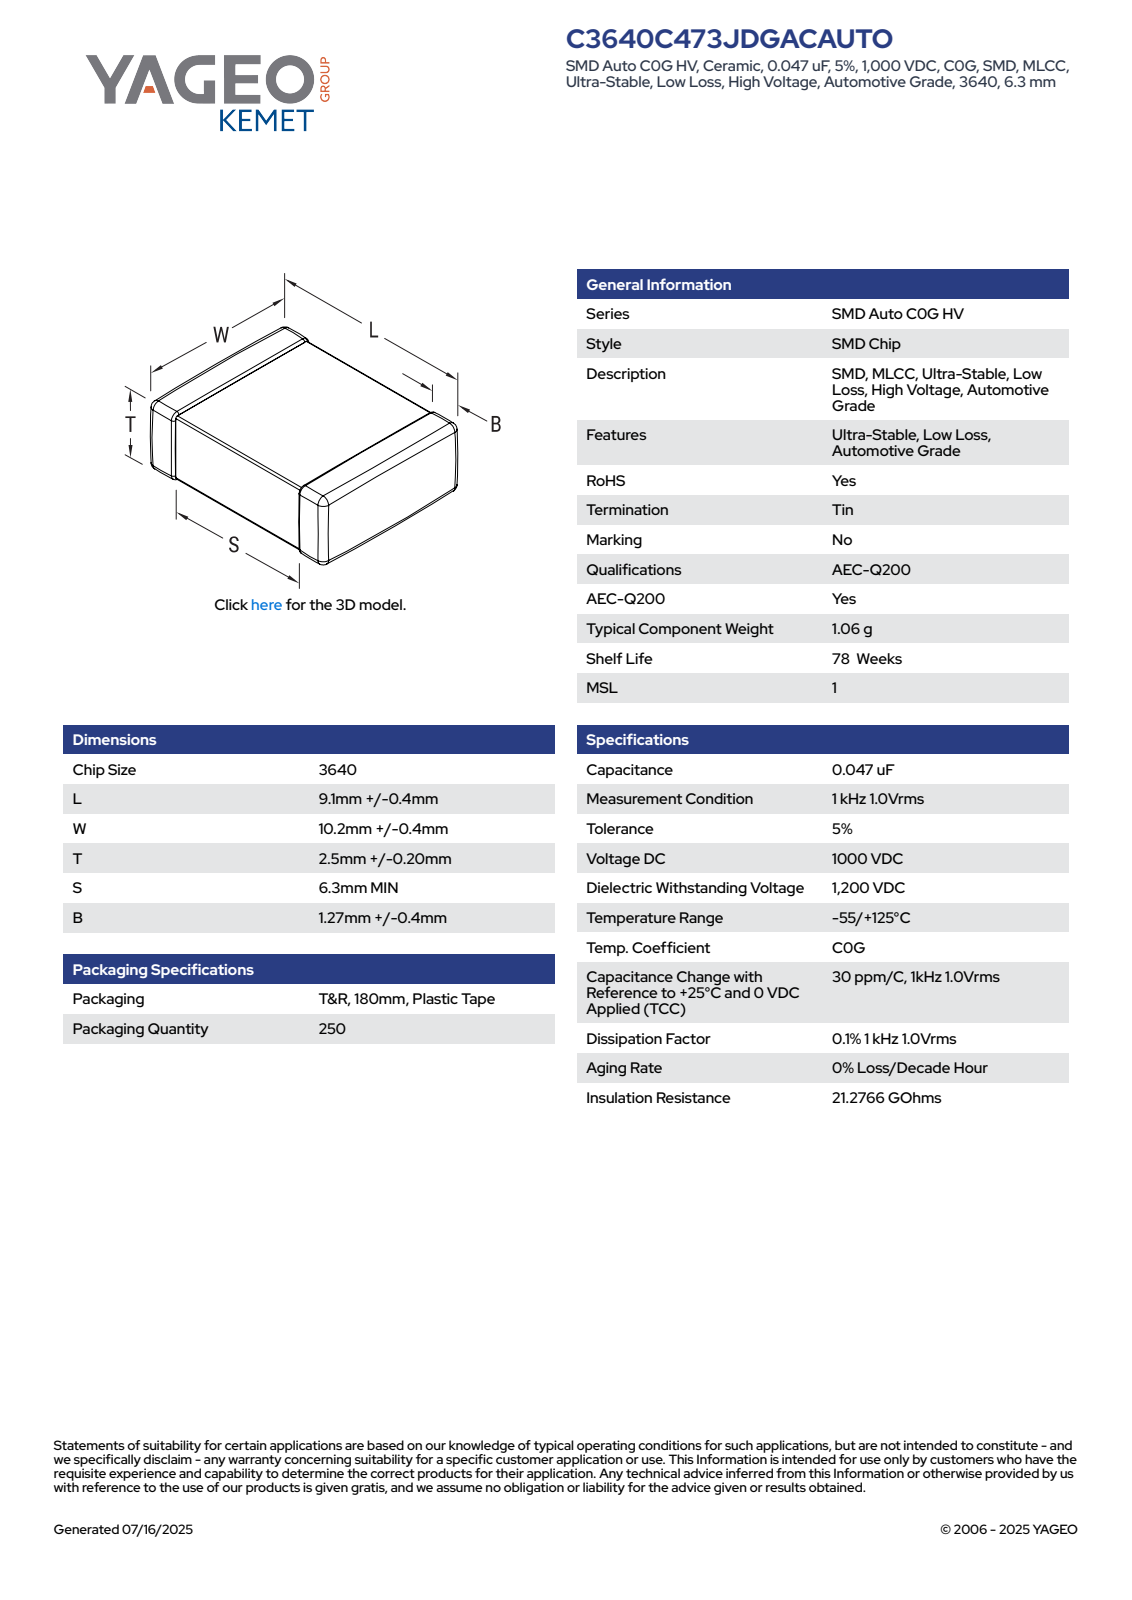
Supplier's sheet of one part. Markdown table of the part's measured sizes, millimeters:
| quantity | value |
| --- | --- |
| part name | CCS_CCSTD_3640_L9.5W10.6T2.7B1.27 |
| STEP written by | SolidWorks 2021 (AUTOMOTIVE_DESIGN) |
| units | millimeters |
| bodies | 4 solids, 125 faces (71 planar, 38 cylindrical, 16 other) |
| overall size | 10.6 × 9.5 × 2.7 |
| volume | 236 mm³ |
| surface area | 311 mm² |
| partial cylindrical surfaces (radius × count) | 0.22 × 24 |
| main face-to-face distances | 2.26, 2.48, 2.7, 9.5, 10.16, 10.38, 10.6, 3.57, 5.93, 5.13 |
